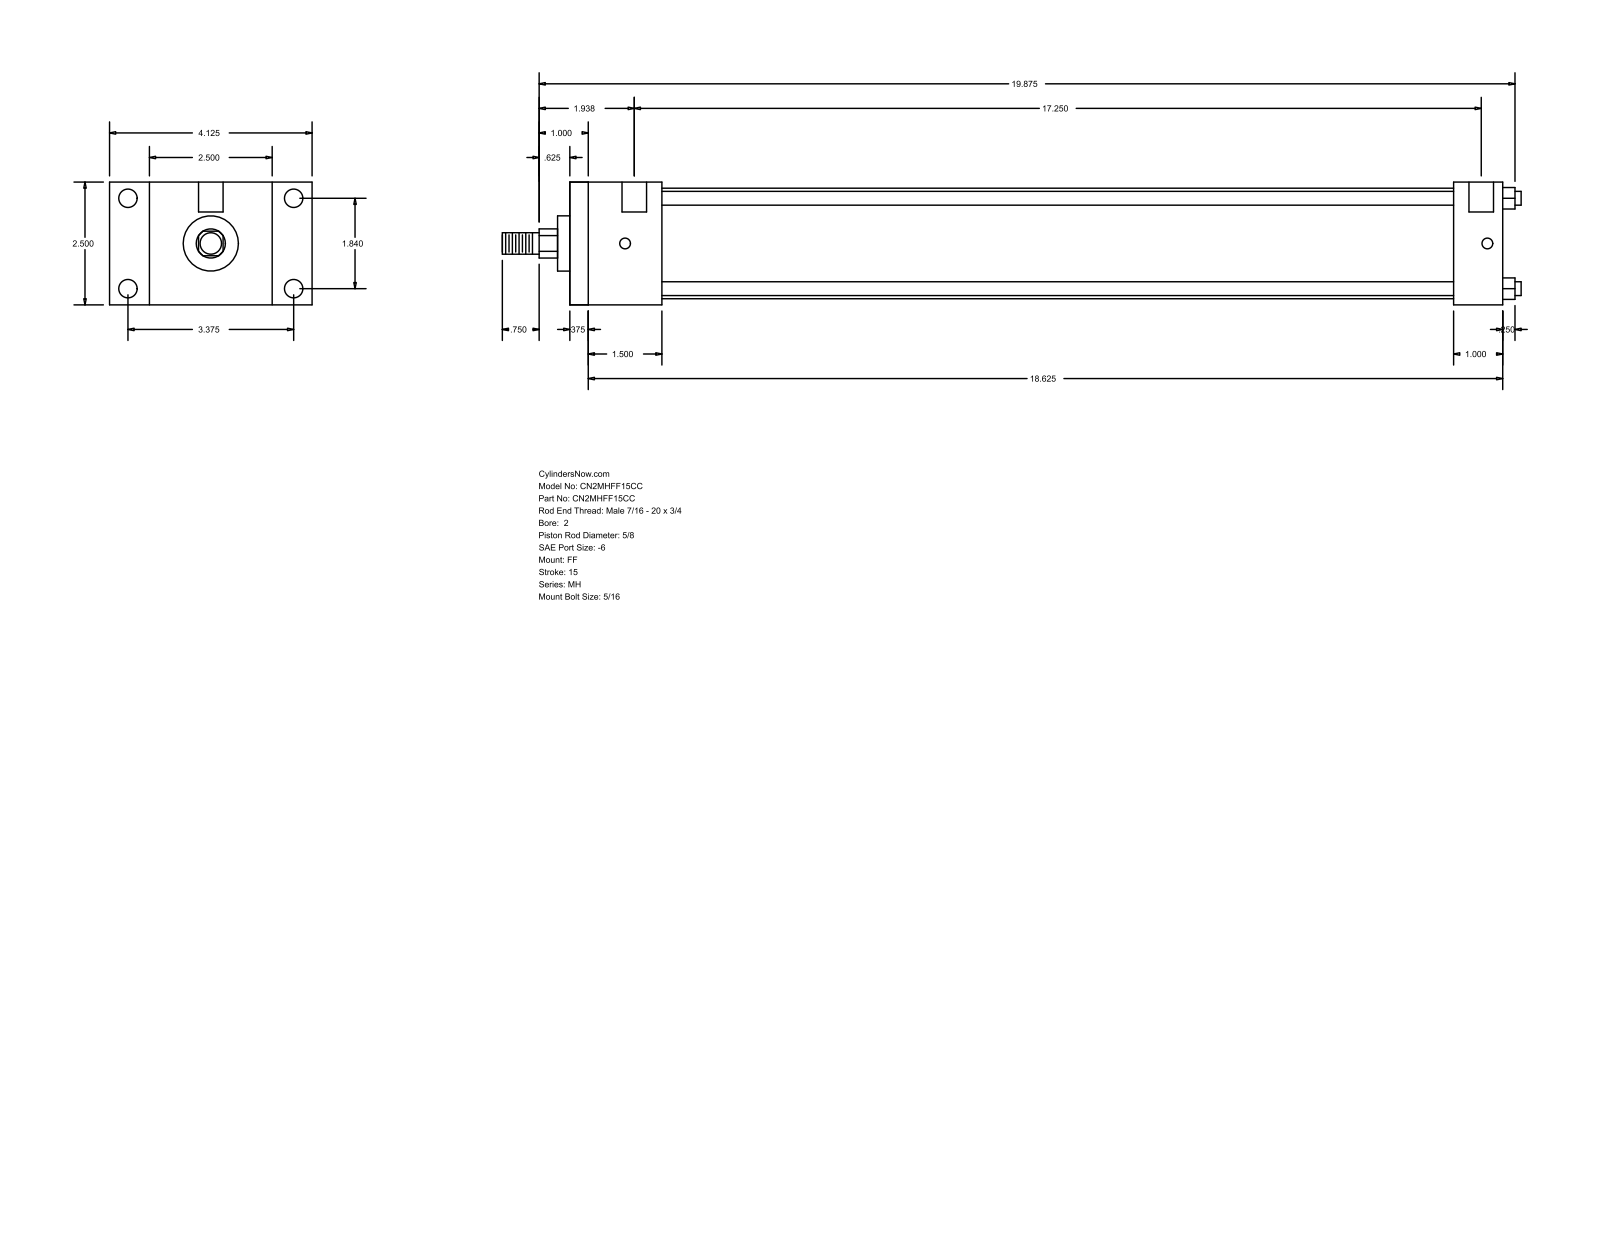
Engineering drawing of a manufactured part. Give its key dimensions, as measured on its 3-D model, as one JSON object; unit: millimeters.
{"part_name": "MH_FF__0200_0.625", "step_written_by": "GSSL Pune (CONFIG_CONTROL_DESIGN)", "units": "millimeters", "bodies": {"solids": 0, "faces": 92, "planar": 64, "cylindrical": 28, "other": 0}, "overall_size": [527.05, 104.78, 63.5], "round_holes": [[5.56, 4], [9.53, 4], [12.7, 2]], "round_bosses_or_shafts": [[7.14, 4], [57.15, 1], [28.57, 1], [15.88, 1], [11.11, 1]], "partial_cylinders_radius": [[7.54, 1]], "face_to_face_distances": [63.5, 482.6, 9.52, 473.08, 38.1, 47.62, 457.19, 447.67, 409.57, 434.98], "hole_center_spacings": [46.74, 85.72, 97.63, 446.09, 3.18, 4.76, 438.15, 441.33]}
